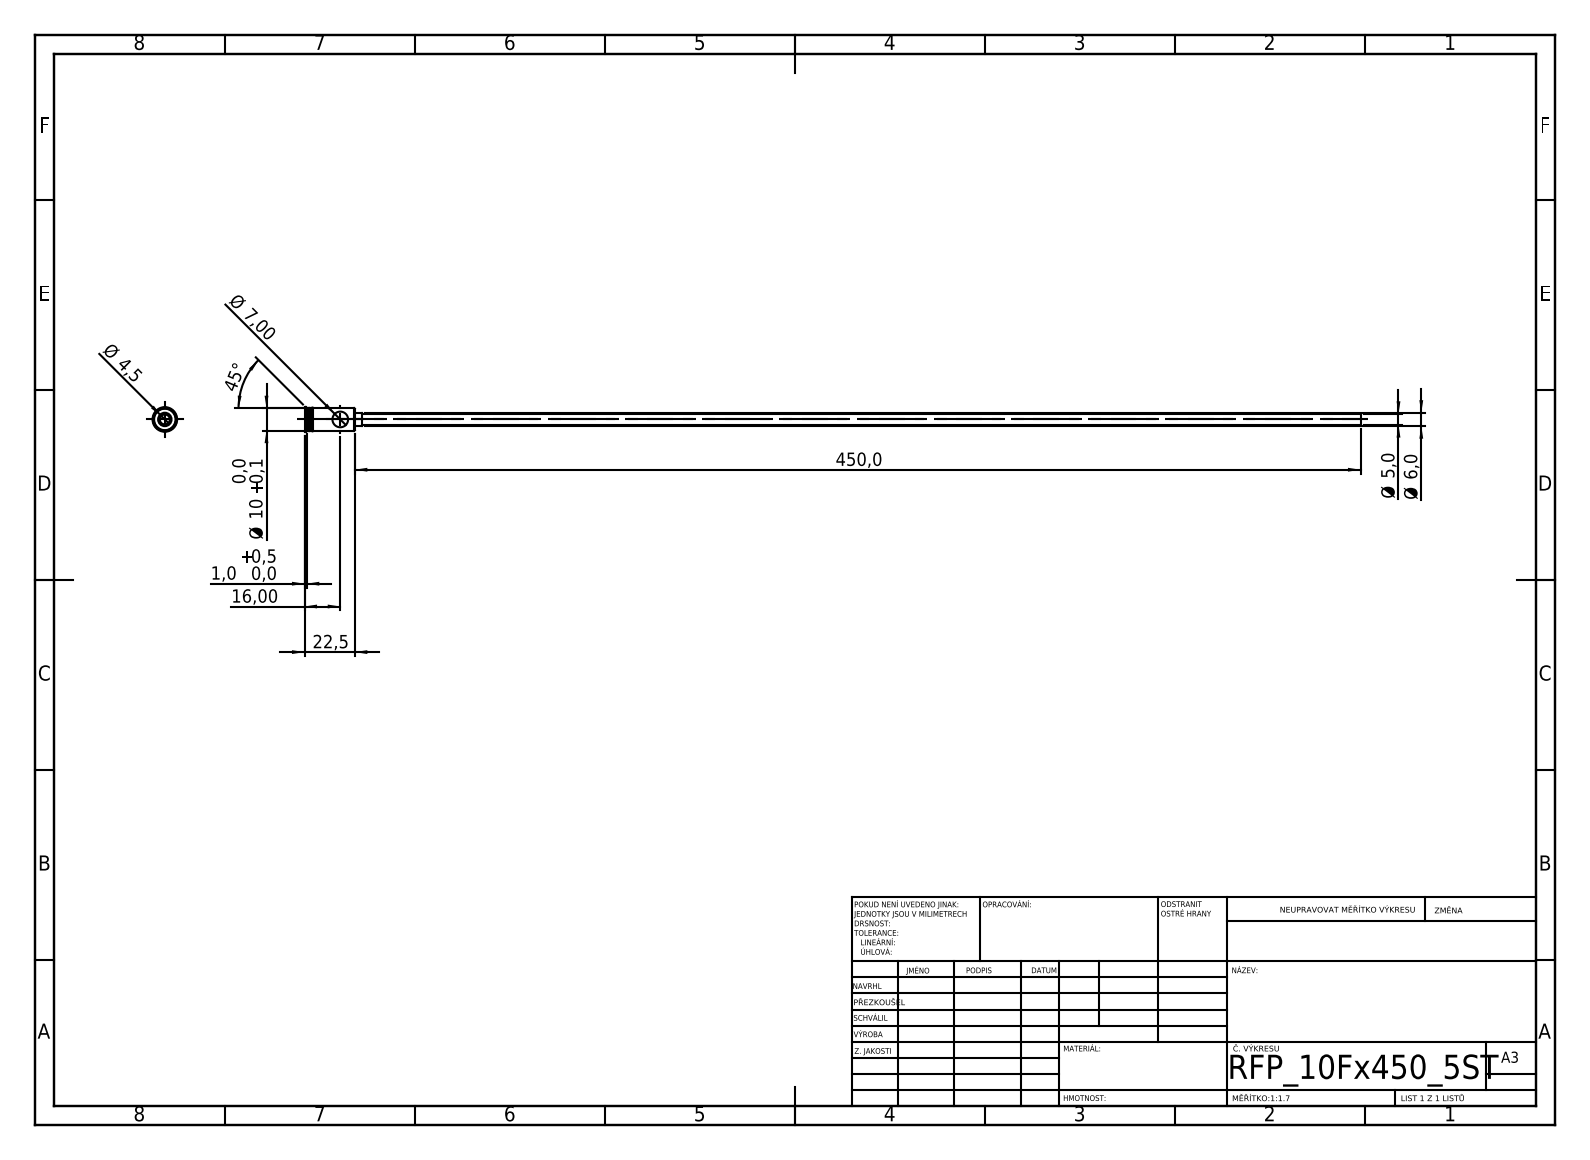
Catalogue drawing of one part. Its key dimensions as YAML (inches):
step_written_by: "SolidWorks 2019 (CONFIG_CONTROL_DESIGN)"
units: inches
bodies: {solids: 1, faces: 44, planar: 20, cylindrical: 16, other: 8}
overall_size: [18.602, 0.433, 0.433]
volume: 0.185
surface_area: 22.49
round_holes:
  - {diameter: 0.177, count: 1}
  - {diameter: 0.276, count: 1}
round_bosses_or_shafts:
  - {diameter: 0.433, count: 1}
  - {diameter: 0.394, count: 1}
  - {diameter: 0.236, count: 1}
  - {diameter: 0.197, count: 1}
face_to_face_distances: [0.886, 0.807, 0.079, 0.213, 0.795, 0.091, 0.118, 0.913, 0.925, 1.004]
